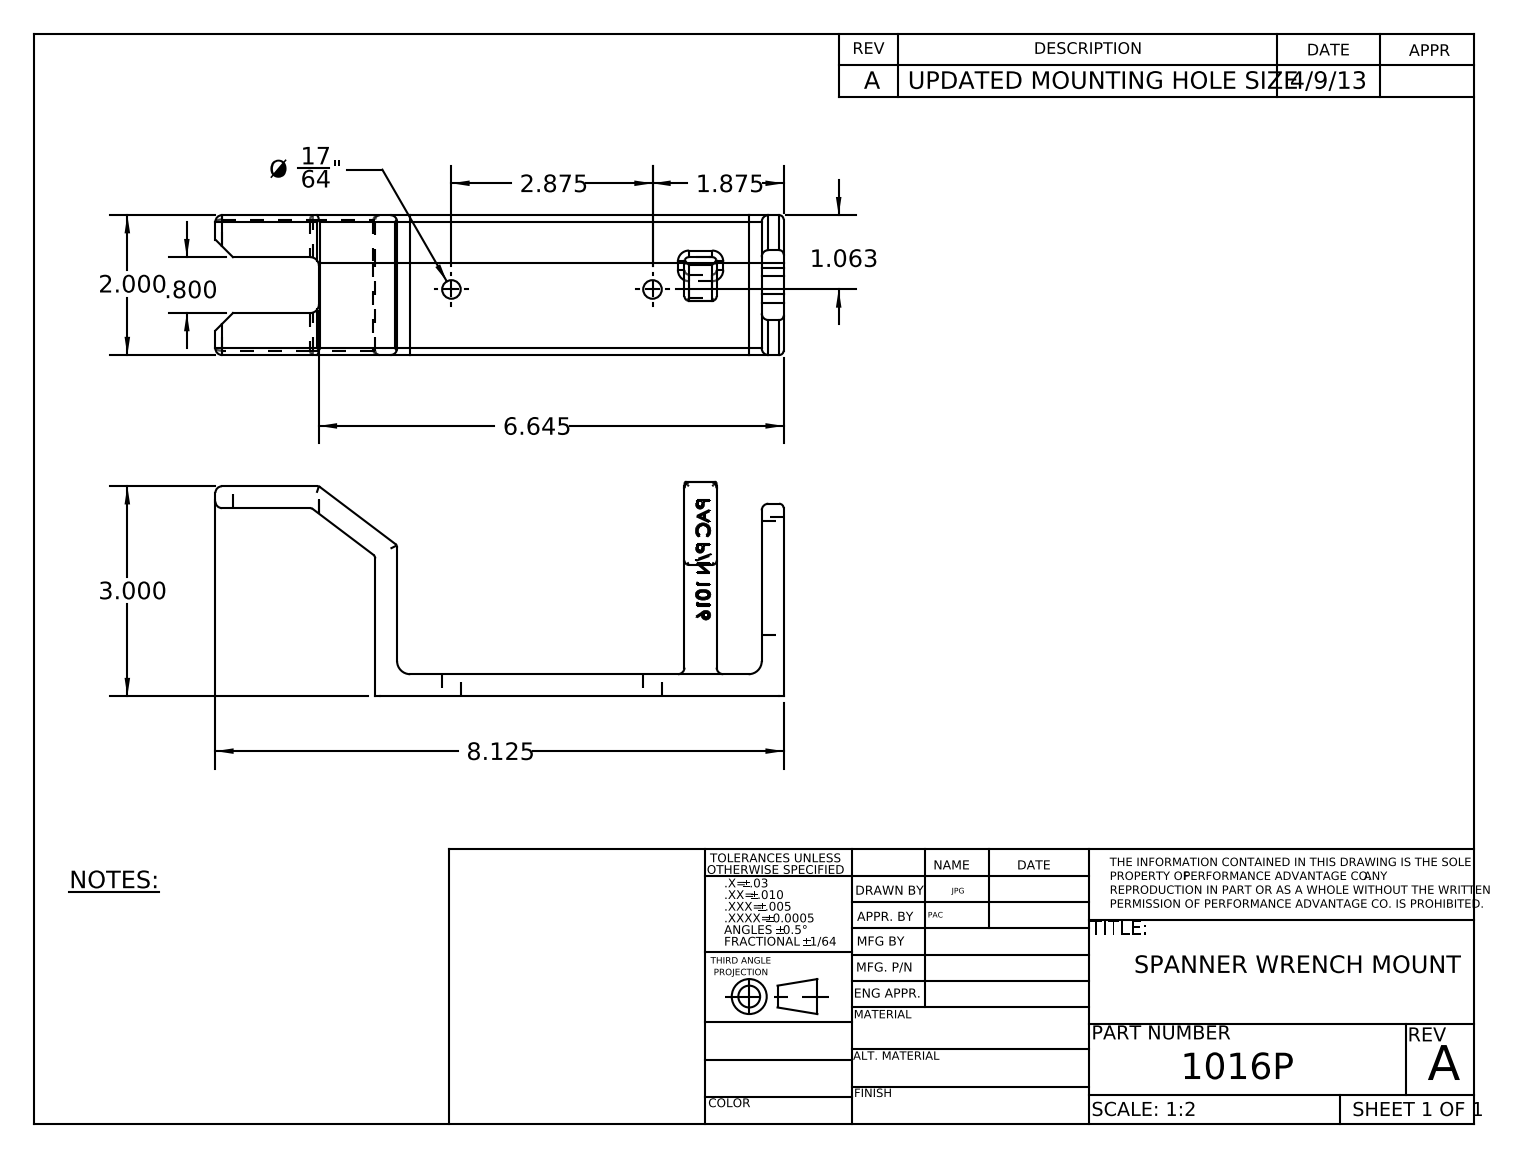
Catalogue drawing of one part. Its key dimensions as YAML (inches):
part_name: "1016"
step_written_by: "SolidWorks 2014 (CONFIG_CONTROL_DESIGN)"
units: inches
bodies: {solids: 2, faces: 243, planar: 119, cylindrical: 65, other: 59}
overall_size: [8.125, 3.063, 2]
volume: 7.607
surface_area: 69.69
round_holes:
  - {diameter: 0.266, count: 2}
partial_cylinders:
  - {radius: 0.094, count: 19}
  - {radius: 0.062, count: 12}
  - {radius: 0.063, count: 8}
  - {radius: 0.125, count: 4}
  - {radius: 0.188, count: 2}
  - {radius: 0.031, count: 1}
  - {radius: 1.875, count: 1}
face_to_face_distances: [0.313, 5.528, 5.84, 5.215, 2.687, 1.313, 2, 0.687, 0.312, 0.6]
hole_center_spacings: [2.875]
